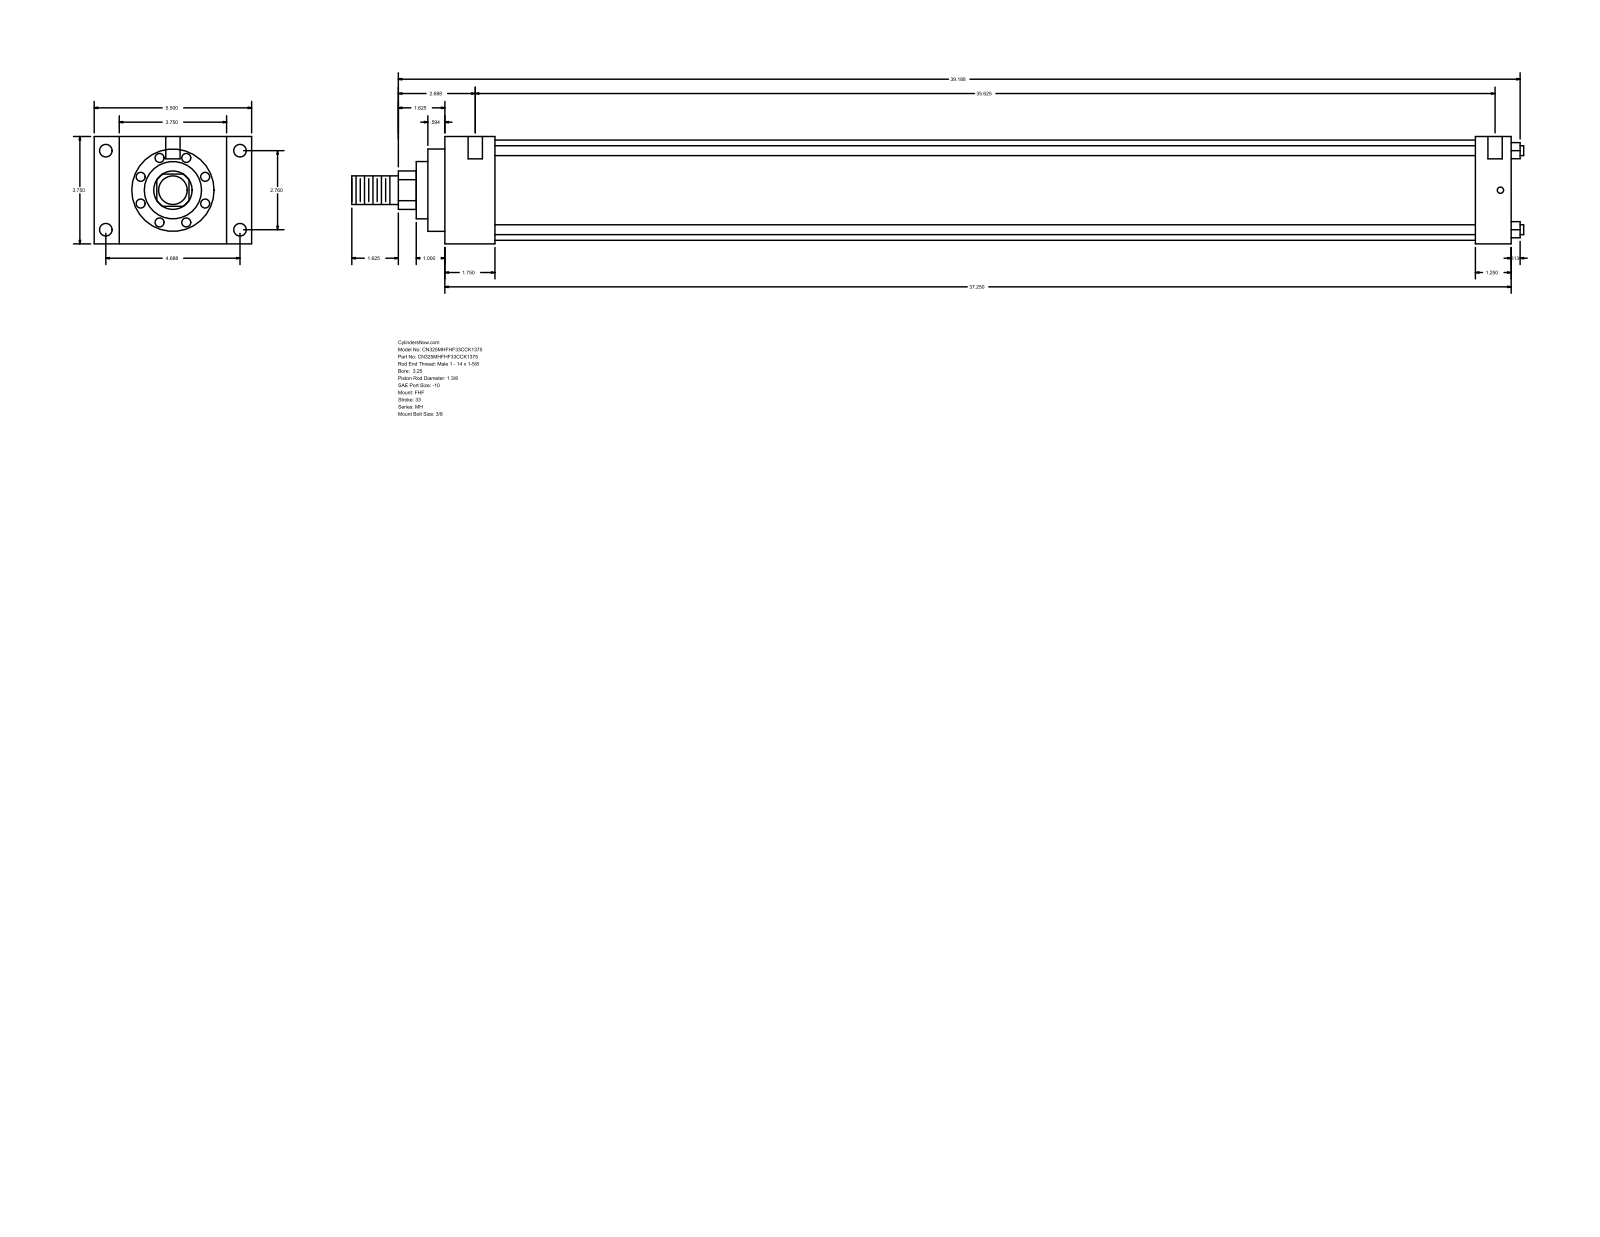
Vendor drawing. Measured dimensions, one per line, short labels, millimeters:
name: MH_FHF__0325_1.375
written by: GSSL Pune (CONFIG_CONTROL_DESIGN)
unit: mm
bodies: 0 solids, 90 faces (61 planar, 29 cylindrical, 0 other)
size: 1039.81 × 139.7 × 95.25
holes: 4× ⌀5.56, 4× ⌀11.13, 2× ⌀12.7
bosses: 4× ⌀8.76, 1× ⌀88.9, 1× ⌀73.03, 1× ⌀50.8, 1× ⌀34.92, 1× ⌀25.4
rounds: 1× R17.06
face distances: 95.24, 946.15, 44.45, 901.7, 22.23, 117.47, 139.7, 914.4, 869.95, 31.75
hole spacings: 70.1, 119.06, 138.16, 911.23, 1.59, 4.76, 904.88, 906.47
